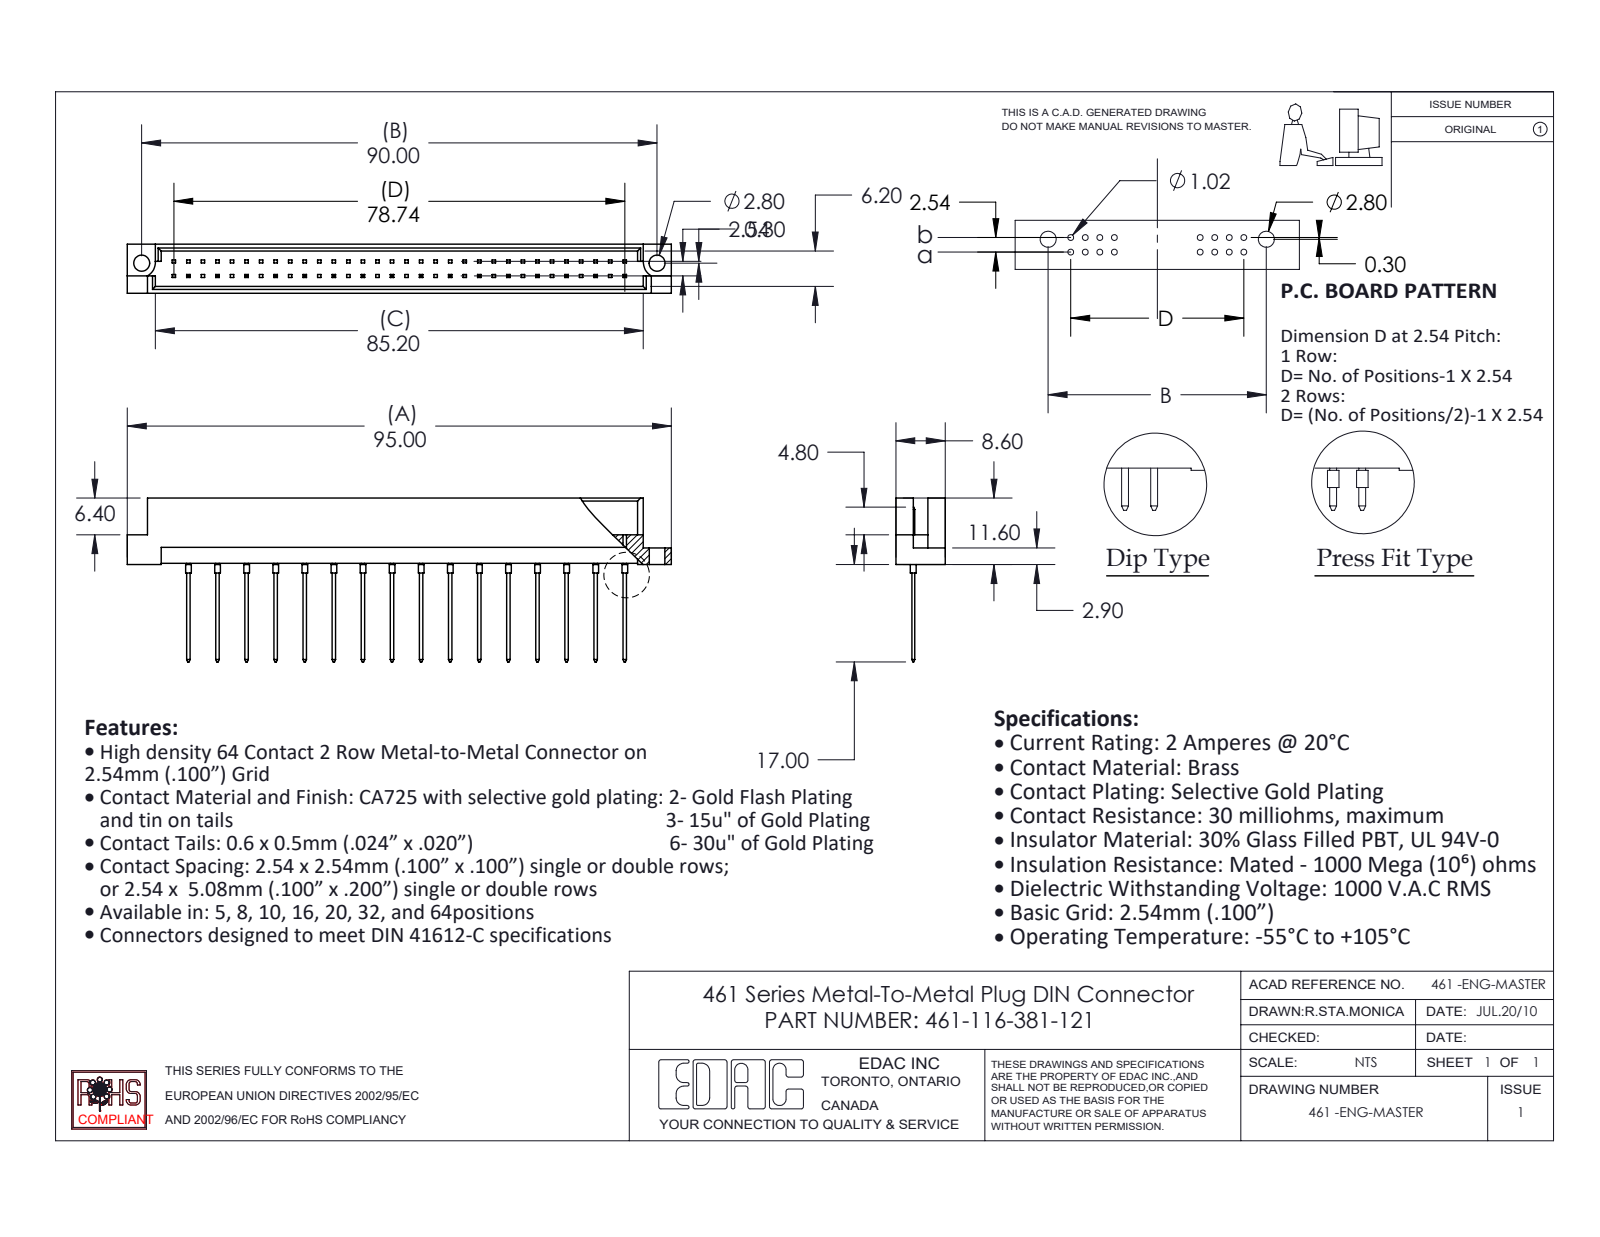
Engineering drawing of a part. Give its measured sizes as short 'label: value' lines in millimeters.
name: 461-290_81; 461 Part_64; 461-116-381-221
written by: SolidWorks 2020 (CONFIG_CONTROL_DESIGN)
unit: mm
bodies: 17 solids, 657 faces (618 planar, 39 cylindrical, 0 other)
size: 95 × 28.6 × 8.6
volume: 4 796 mm³; area: 6 654 mm²
holes: 2× ⌀2.8
bosses: 16× ⌀1
rounds: 2× R2.8
face distances: 1.2, 7.4, 8.6, 6.2, 5, 3.28, 5.32, 2.08, 4.12, 2.78
hole spacings: 90
